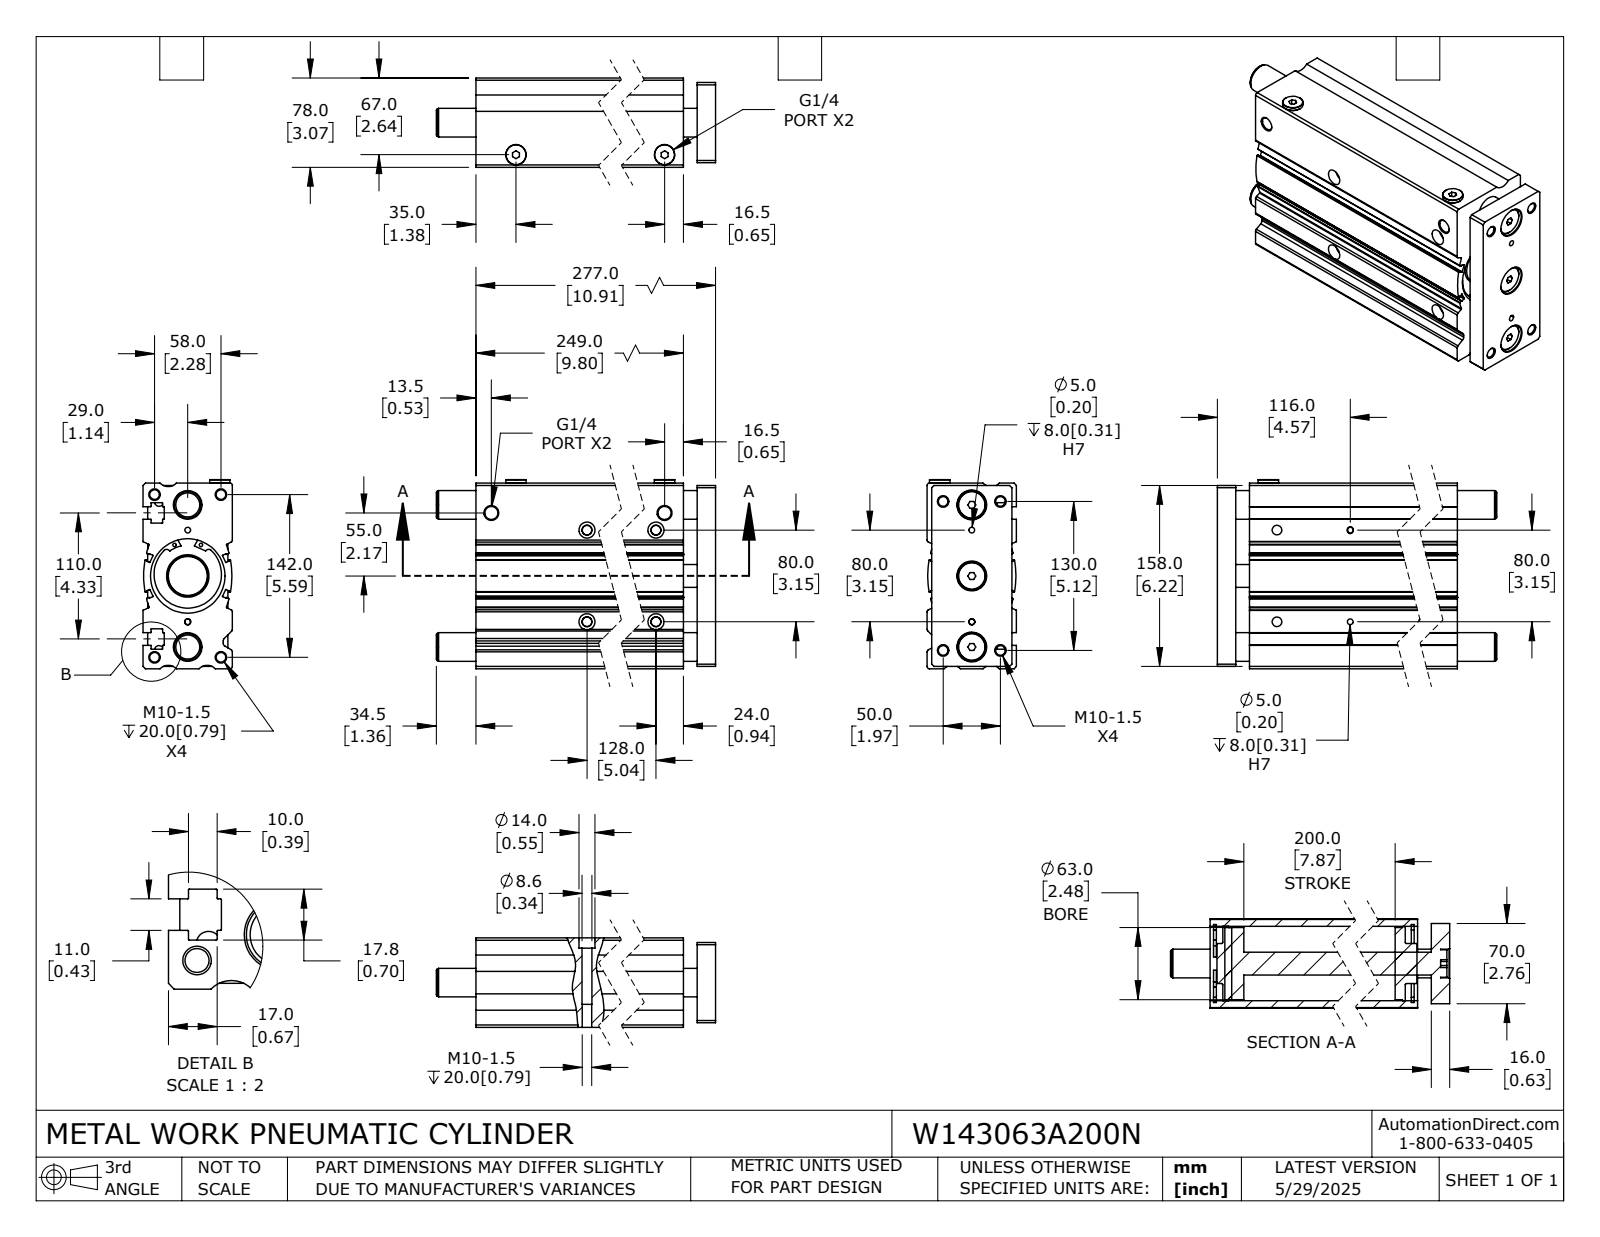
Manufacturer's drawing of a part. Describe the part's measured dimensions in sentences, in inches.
The part is named "W143063A200N; W143063A200N_BODY; W143063A200N_ROD". Its 3-D file was written by "SolidWorks 2024 (CONFIG_CONTROL_DESIGN)". It is 6 solids with 454 faces: 182 planar, 216 cylindrical and 56 other. Overall it measures 12.264 by 6.496 by 3.071 inches. Its volume is 147.8 cubic inches and its surface area 630.8 square inches. Round holes: 12 of diameter 0.33, 4 of diameter 0.118, 4 of diameter 0.197, 4 of diameter 0.339, 4 of diameter 0.551, 3 of diameter 0.984, 2 of diameter 0.448, 1 of diameter 2.559. Round bosses or shafts: 3 of diameter 0.945, 2 of diameter 0.697, 1 of diameter 2.677, 1 of diameter 2.551, 1 of diameter 2.48, 1 of diameter 1.378, 1 of diameter 0.787. Partial cylindrical surfaces (rounded edges, fillets, slot ends): 44 of radius 0.012, 12 of radius 0.02, 8 of radius 0.079, 4 of radius 0.098, 4 of radius 0.118, 3 of radius 0.394, 2 of radius 0.124, 2 of radius 1.157. The main face-to-face distances are 3.071, 6.378, 0.63, 4.331, 0.134, 0.567, 0.728, 0.472, 1.102, 10.906. The hole center spacings are 0.284, 0.682, 0.991, 1.158, 1.195, 1.392, 1.448, 1.585.
